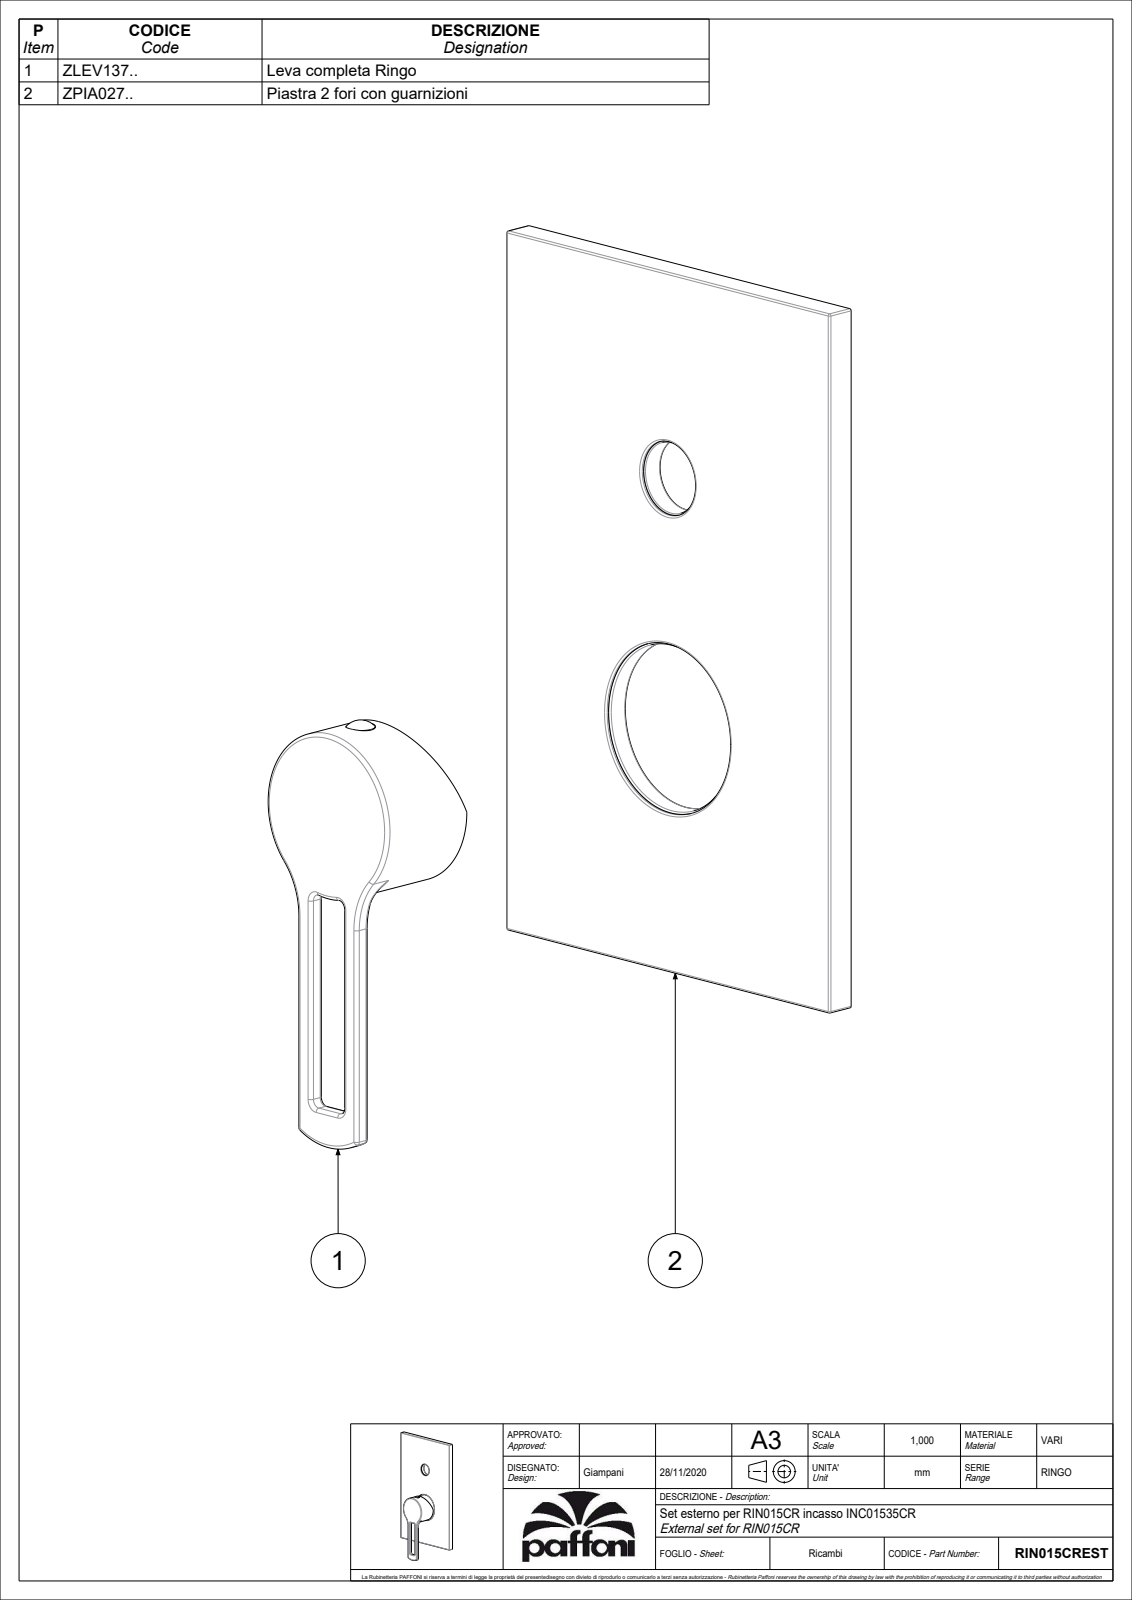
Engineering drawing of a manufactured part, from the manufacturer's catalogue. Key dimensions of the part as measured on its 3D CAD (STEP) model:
Part name (STEP PRODUCT): RIN015CREST
STEP written by: CREO PARAMETRIC BY PTC INC, 2020044 (CONFIG_CONTROL_DESIGN)
Units: millimetres
Bodies: 2 solids, 293 faces (77 planar, 95 cylindrical, 121 other)
Overall size (bounding box): 214 × 120 × 39.5
Volume: 131 375 mm³ · Surface area: 68 413 mm²
Round holes (diameter × count): ⌀3 ×1, ⌀7.8 ×1, ⌀19.2 ×1, ⌀20 ×1, ⌀23.2 ×1, ⌀45 ×1, ⌀46 ×1
Round bosses / shafts (diameter × count): ⌀51 ×1, ⌀49 ×1, ⌀44.8 ×1, ⌀25 ×1, ⌀23 ×1, ⌀7.6 ×1, ⌀5.5 ×1, ⌀5 ×1
Partial cylindrical surfaces — rounded edges, fillets, slot ends (radius × count): R1 ×20, R0.5 ×16, R2 ×4, R20 ×2, R21.67 ×1
Main face-to-face distances: 7.5, 2.5, 5, 0.5, 34, 31.5, 22.5, 39, 97.5, 8
Hole centre spacings: 68
